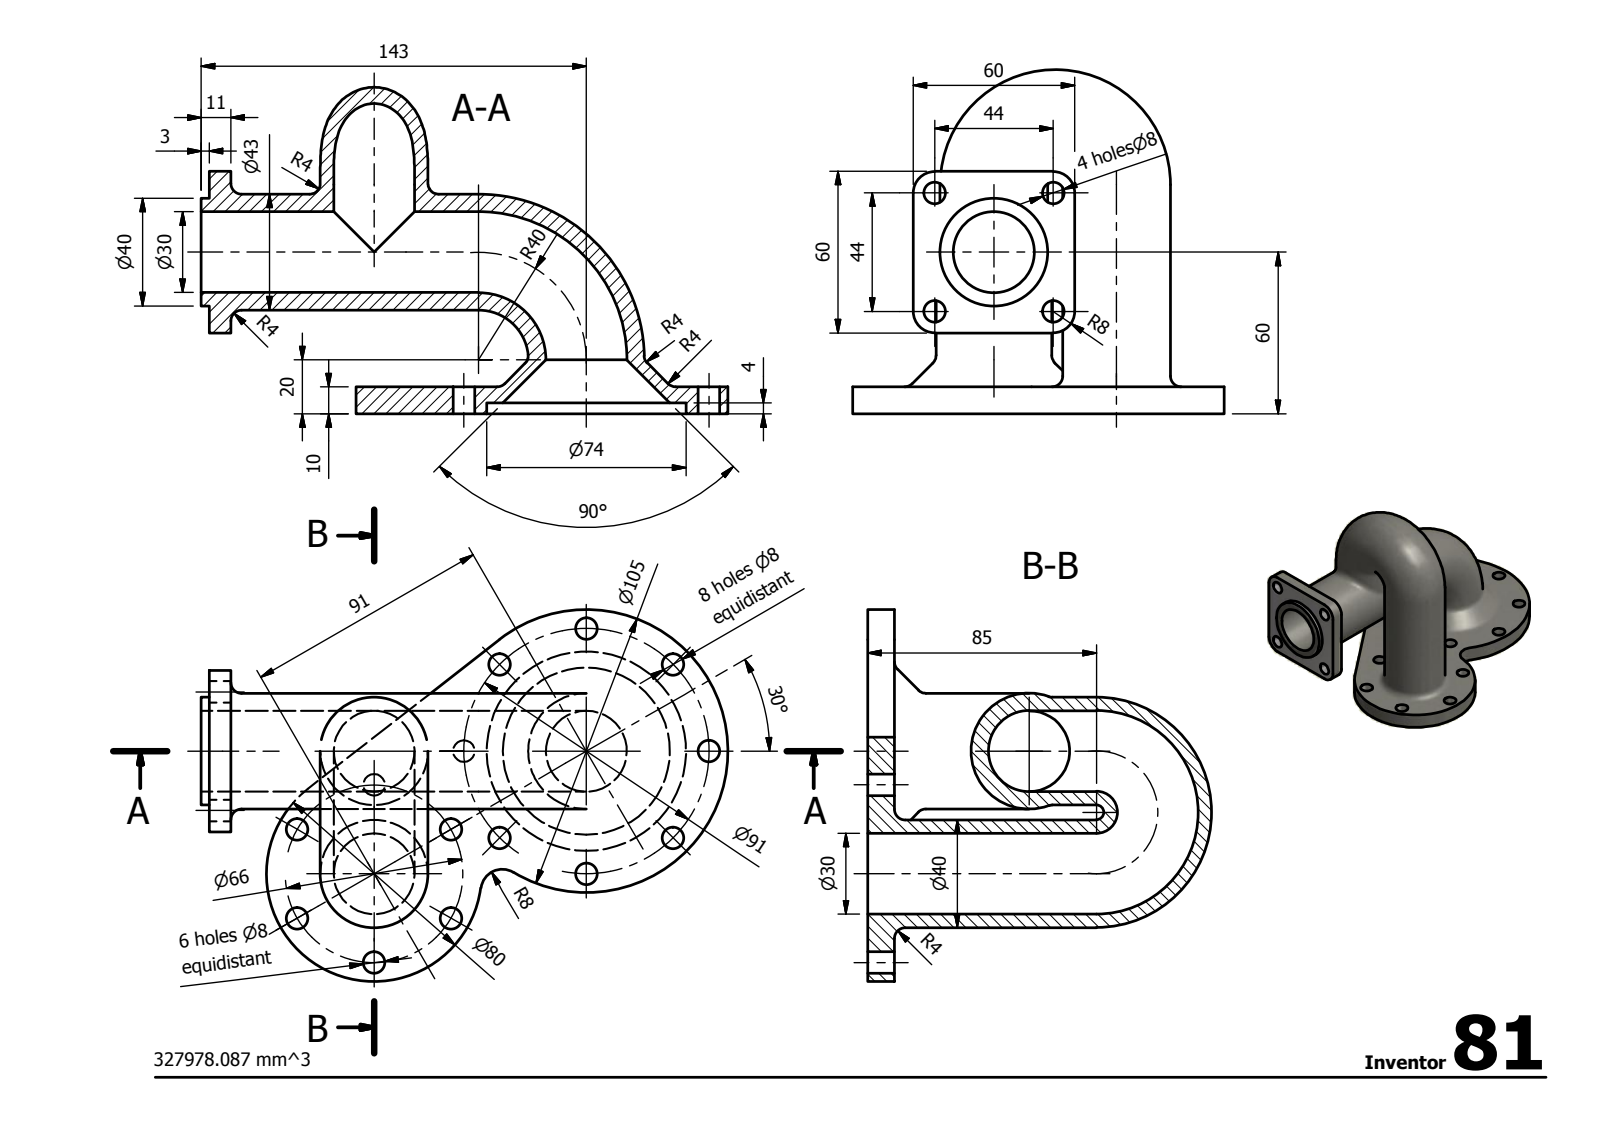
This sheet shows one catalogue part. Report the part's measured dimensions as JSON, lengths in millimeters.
{"step_written_by": "Autodesk Inventor 2014 (AUTOMOTIVE_DESIGN)", "units": "millimeters", "bodies": {"solids": 1, "faces": 59, "planar": 11, "cylindrical": 34, "other": 14}, "overall_size": [195.5, 138, 127.75], "volume_mm3": 327980, "surface_area_mm2": 111510, "round_holes": [[8, 18], [30, 3], [74, 1]], "round_bosses_or_shafts": [[40, 3], [43, 1]], "partial_cylinders_radius": [[8, 5], [40, 1], [52.5, 1]], "face_to_face_distances": [10, 8, 4, 6, 60, 3, 11, 30, 90, 26], "hole_center_spacings": [33, 45.5, 91, 34.82, 57.16, 64.35, 84.07, 31.11]}
